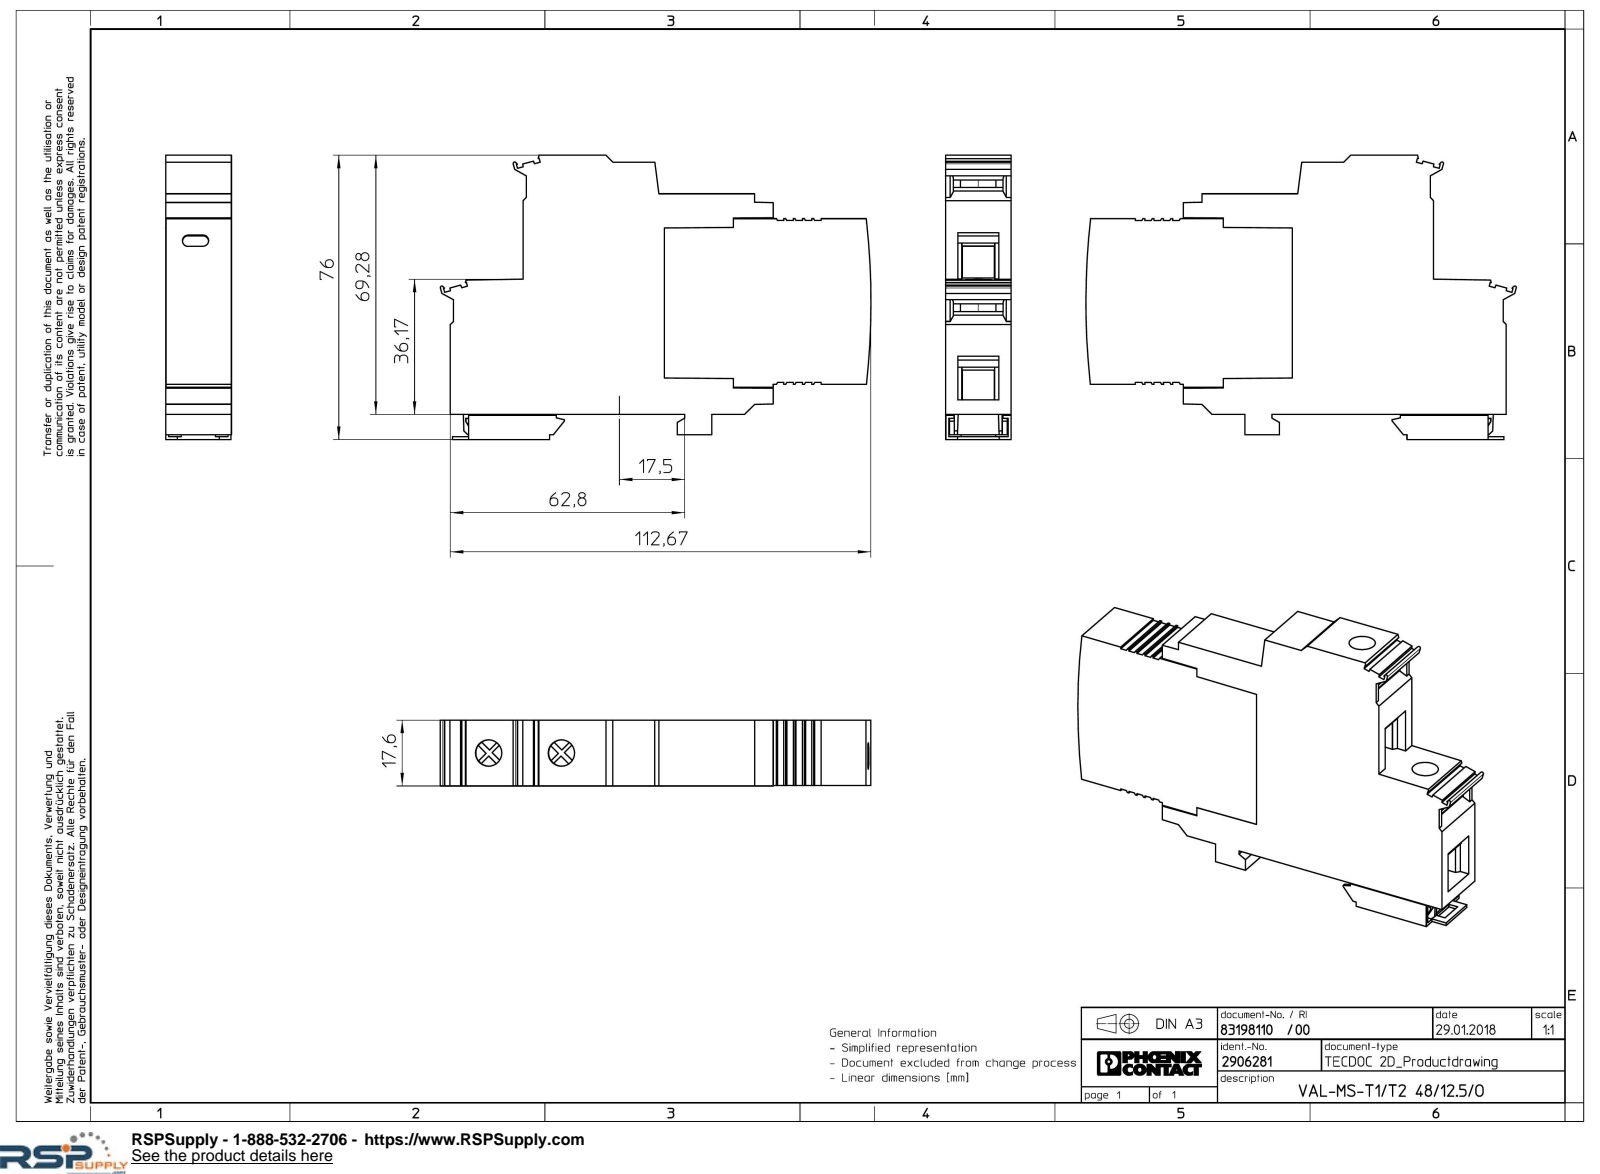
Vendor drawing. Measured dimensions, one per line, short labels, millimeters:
name: VAL_MS_T1_T2_48_12.5_O-select
written by: Creo Elements/Direct Modeling 18.1I 14-Aug-2016 (C) Parametric Technology GmbH (AUTOMOTIVE_DESIGN)
unit: mm
bodies: 1 solid, 270 faces (257 planar, 11 cylindrical, 2 other)
size: 115.33 × 76 × 17.6
volume: 105 537 mm³; area: 24 256 mm²
holes: 2× ⌀7.06
bosses: 2× ⌀9.5
rounds: 2× R0.4, 1× R200
face distances: 17.6, 17.5, 0.8, 58.99, 13.95, 52.33, 6.66, 33.15, 2.01, 6.72
hole spacings: 20.07
